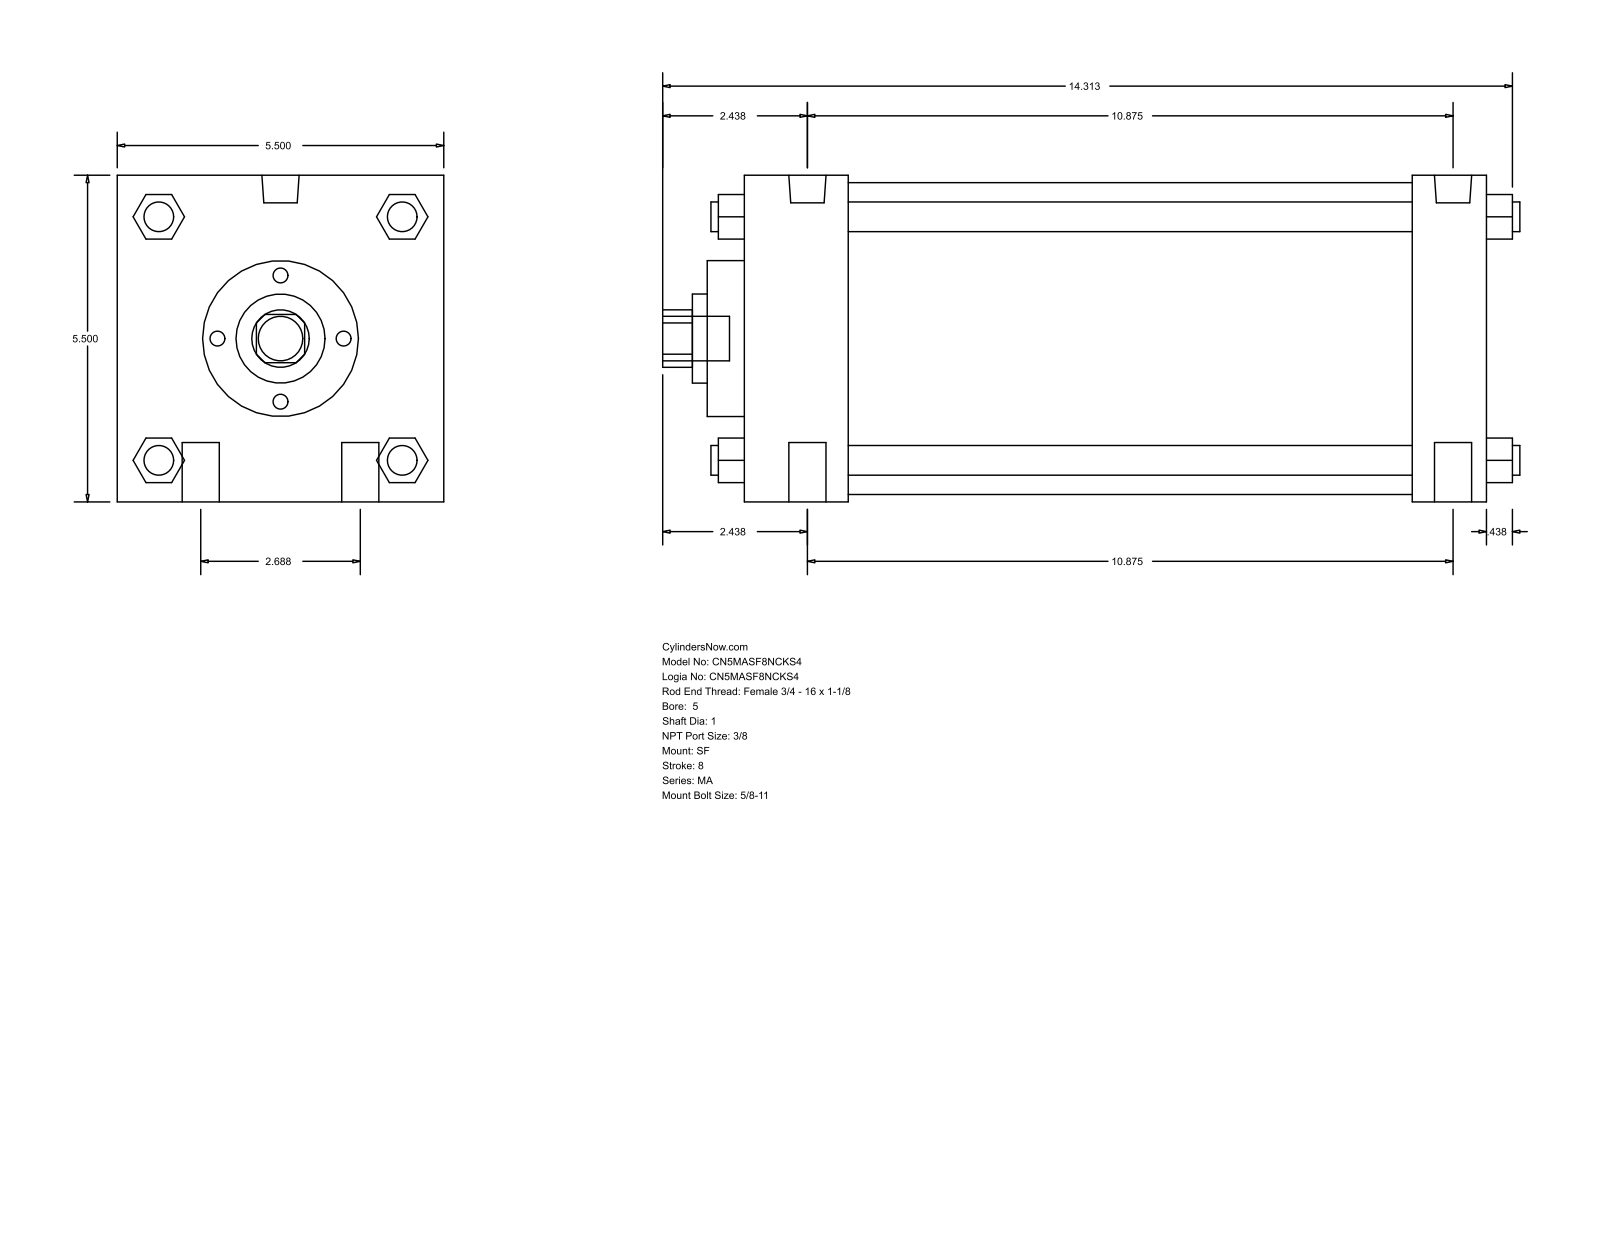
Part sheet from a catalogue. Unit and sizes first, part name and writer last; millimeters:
Units: millimetres
Overall size (bounding box): 366.71 × 139.7 × 139.7
Round holes (diameter × count): ⌀25.4 ×1, ⌀38.1 ×1, ⌀66.67 ×1, ⌀133.35 ×1
Round bosses / shafts (diameter × count): ⌀15.88 ×4, ⌀12.7 ×4, ⌀15.93 ×2, ⌀11.11 ×2, ⌀19.05 ×1
Partial cylindrical surfaces — rounded edges, fillets, slot ends (radius × count): R12.29 ×1
Main face-to-face distances: 139.7, 317.51, 44.46, 285.76, 241.3, 273.05, 31.75, 15.87, 60.33, 301.63
Bodies: 0 solids, 126 faces (95 planar, 31 cylindrical, 0 other)
Part name (STEP PRODUCT): MA_SF__0500_1
STEP written by: GSSL Pune (CONFIG_CONTROL_DESIGN)
